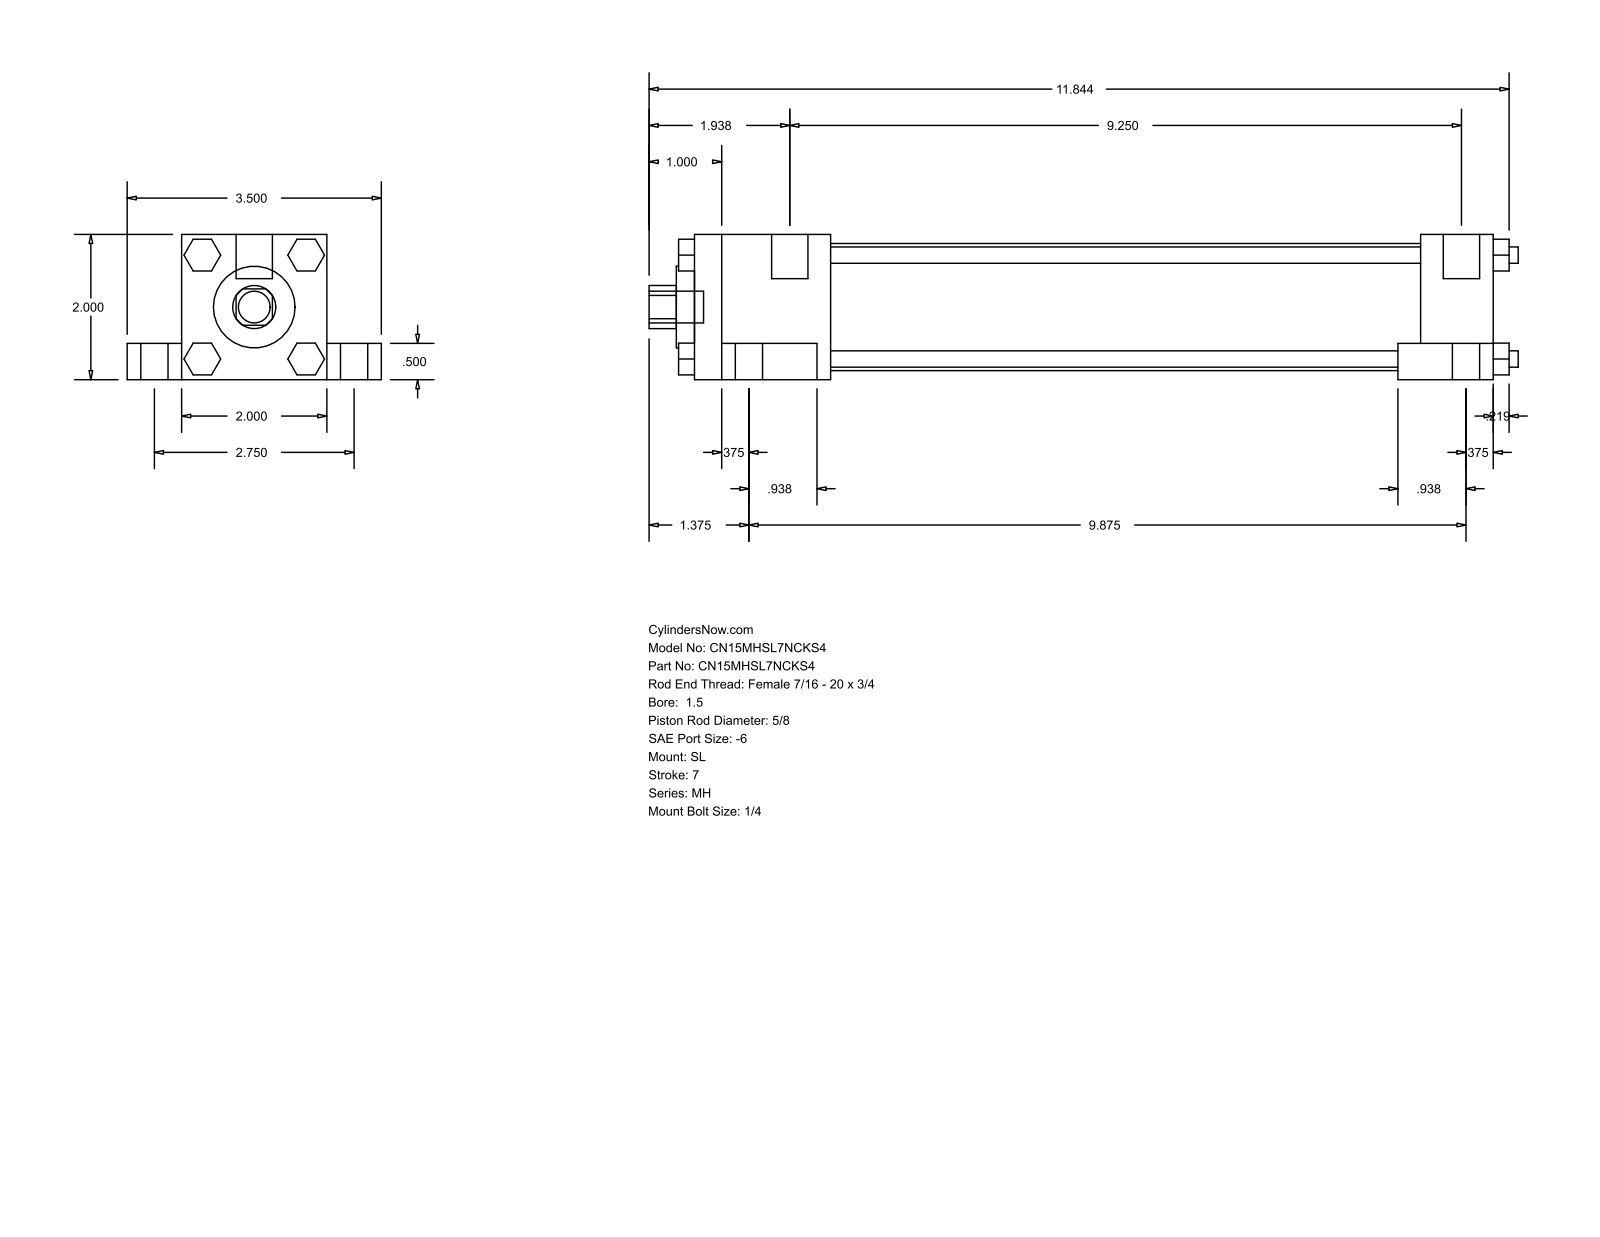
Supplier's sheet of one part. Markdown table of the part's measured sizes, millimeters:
| quantity | value |
| --- | --- |
| part name | MH_SL__0150_0.625 |
| STEP written by | GSSL Pune (CONFIG_CONTROL_DESIGN) |
| units | millimeters |
| bodies | 0 solids, 148 faces (112 planar, 36 cylindrical, 0 other) |
| overall size | 304.01 × 88.9 × 50.8 |
| round holes (diameter × count) | 15.88 × 1, 28.57 × 1, 44.45 × 1 |
| round bosses / shafts (diameter × count) | 15.88 × 4, 9.53 × 4, 5.71 × 4, 5.56 × 4, 12.7 × 2, 11.11 × 1 |
| partial cylindrical surfaces (radius × count) | 7.54 × 1 |
| main face-to-face distances | 50.8, 38.1, 19.05, 12.7, 69.85, 279.39, 9.52, 254, 25.39, 47.62 |
